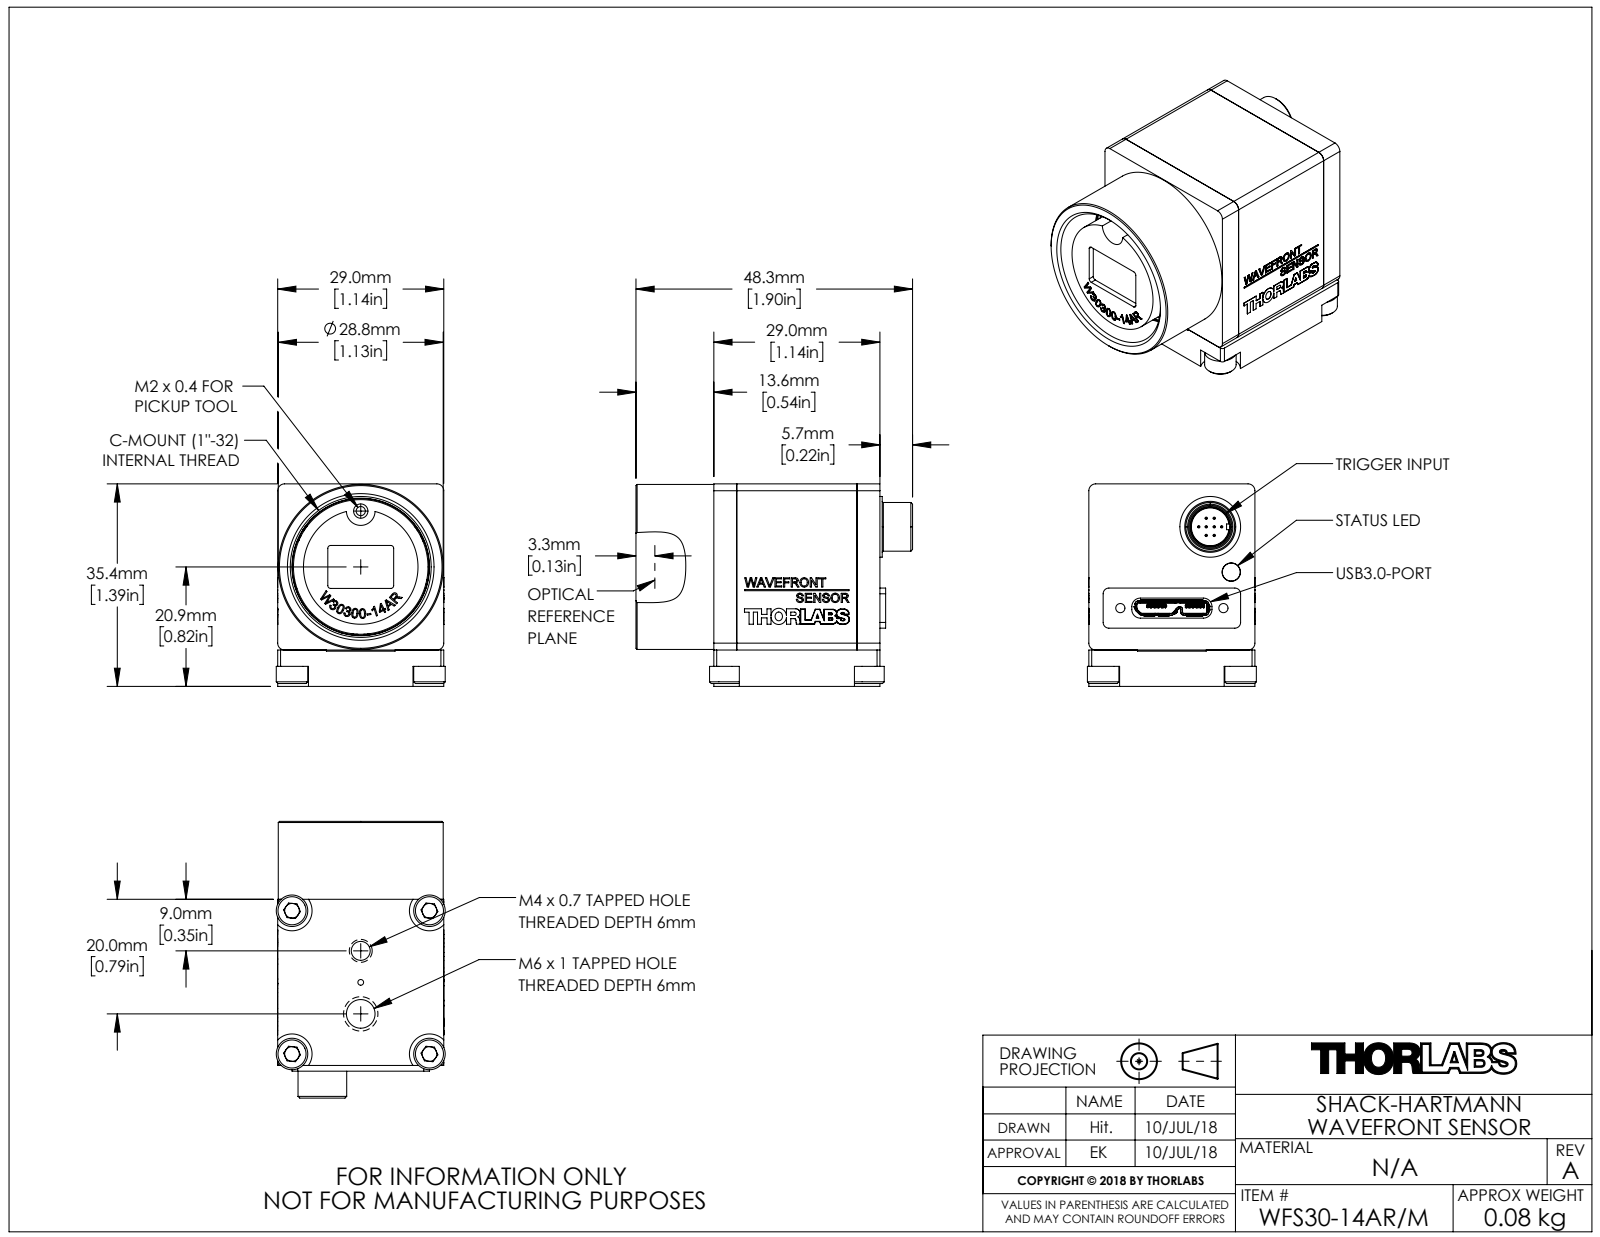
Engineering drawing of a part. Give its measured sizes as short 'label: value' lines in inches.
name: MTN008523-E0W
written by: SolidWorks 2016 (AUTOMOTIVE_DESIGN)
unit: in
bodies: 0 solids, 2630 faces (1902 planar, 409 cylindrical, 319 other)
size: 1.902 × 1.392 × 1.161
holes: 11× ⌀0.126, 5× ⌀0.098, 3× ⌀0.063, 3× ⌀0.075, 1× ⌀0.037, 1× ⌀0.039, 1× ⌀0.059, 1× ⌀0.13, 1× ⌀0.197, 1× ⌀0.268, 1× ⌀0.315, 1× ⌀0.591
bosses: 8× ⌀0.016, 6× ⌀0.039, 5× ⌀0.118, 4× ⌀0.217, 1× ⌀1.134, 1× ⌀0.941, 1× ⌀0.925, 1× ⌀0.787
rounds: 31× R0.008, 29× R0.006, 29× R0.02, 12× R0.012, 11× R0.039, 10× R0.059, 8× R0.004, 8× R0.024
face distances: 1.142, 0.024, 1.118, 0.25, 0.189, 1.392, 0.103, 1.094, 0.692, 0.881
hole spacings: 0.384, 0.741, 0.383, 0.543, 0.665, 0.198, 0.547, 0.682
